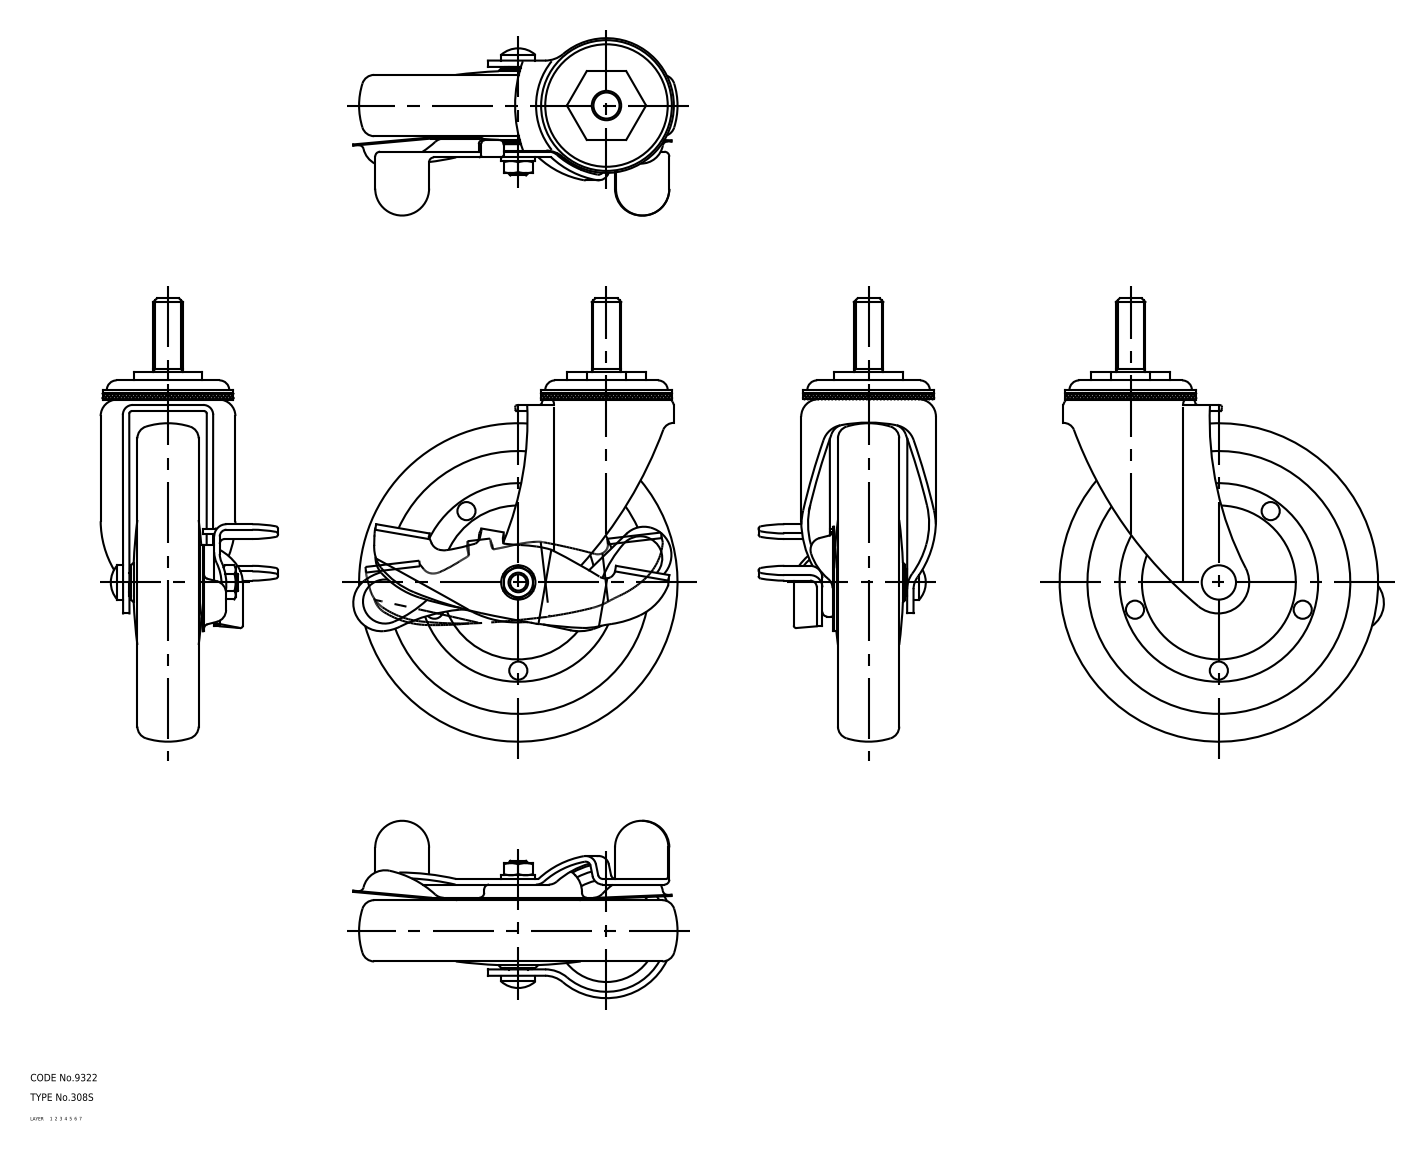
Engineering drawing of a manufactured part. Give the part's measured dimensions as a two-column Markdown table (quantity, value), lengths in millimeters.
| quantity | value |
| --- | --- |
| part name | lever; wheel; plate; main shaft (+2 more) |
| STEP written by | CADfix (AUTOMOTIVE_DESIGN) |
| units | millimeters |
| bodies | 6 solids, 373 faces (0 planar, 0 cylindrical, 373 other) |
| overall size | 181 × 132.37 × 72.41 |
| volume | 316 987 mm³ |
| surface area | 86 436 mm² |
